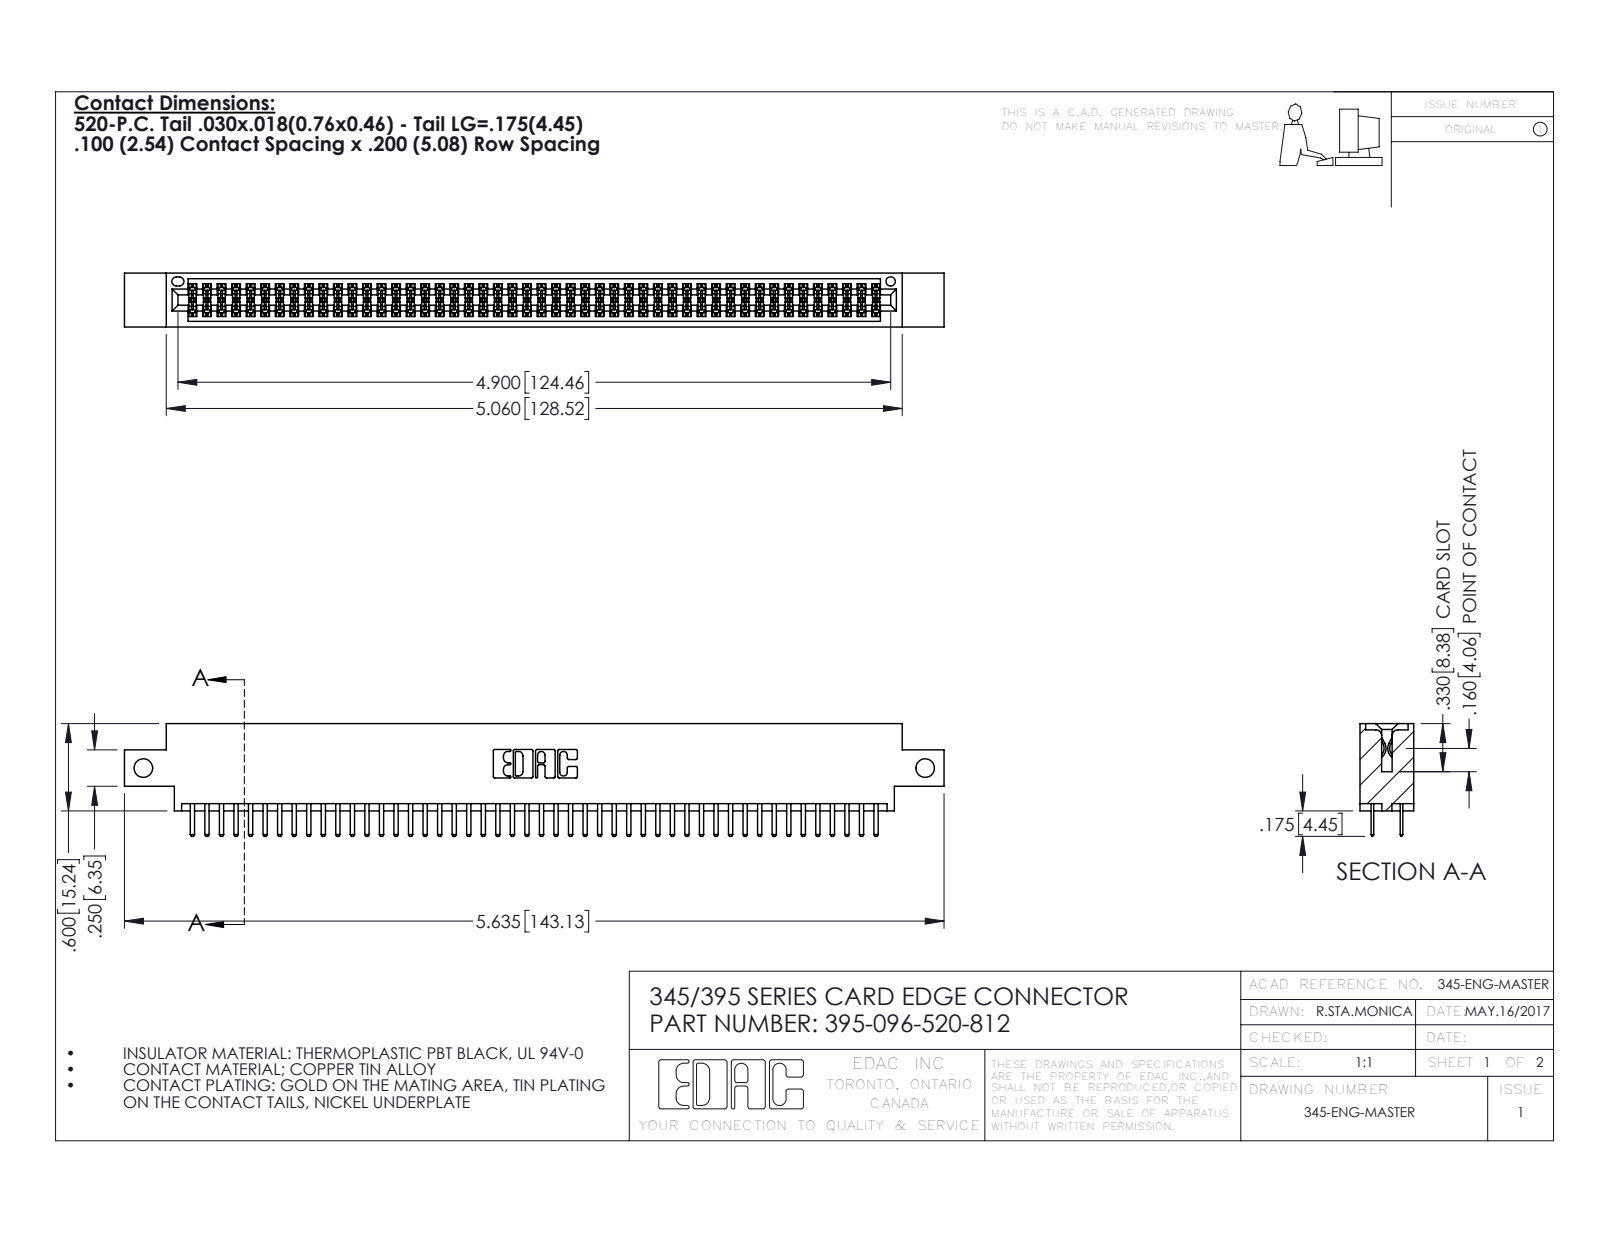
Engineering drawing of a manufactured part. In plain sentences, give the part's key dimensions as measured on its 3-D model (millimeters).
The part is named "345 Part_0.170 Offset - Side Mount; 345-292-001_345-293-120; 395-096-520-812". Its 3-D file was written by "SolidWorks 2016 (CONFIG_CONTROL_DESIGN)". It is 97 solids with 5314 faces: 3444 planar, 1870 cylindrical and 0 other. Overall it measures 143.1 by 19.7 by 9.4 millimeters. Its volume is 13 700 cubic millimeters and its surface area 20 310 square millimeters. Round holes: 2 of diameter 3.3, 1 of diameter 1.6. Partial cylindrical surfaces (rounded edges, fillets, slot ends): 145 of radius 0.2, 100 of radius 0.3, 22 of radius 0.3, 6 of radius 0.2, 6 of radius 0.8, 3 of radius 0.7, 2 of radius 0.4, 2 of radius 0.5. The main face-to-face distances are 1.8, 7.6, 5.1, 9.4, 2.5, 6.9, 0.6, 5.7, 0.6, 4.4. The hole center spacings are 136.5.
